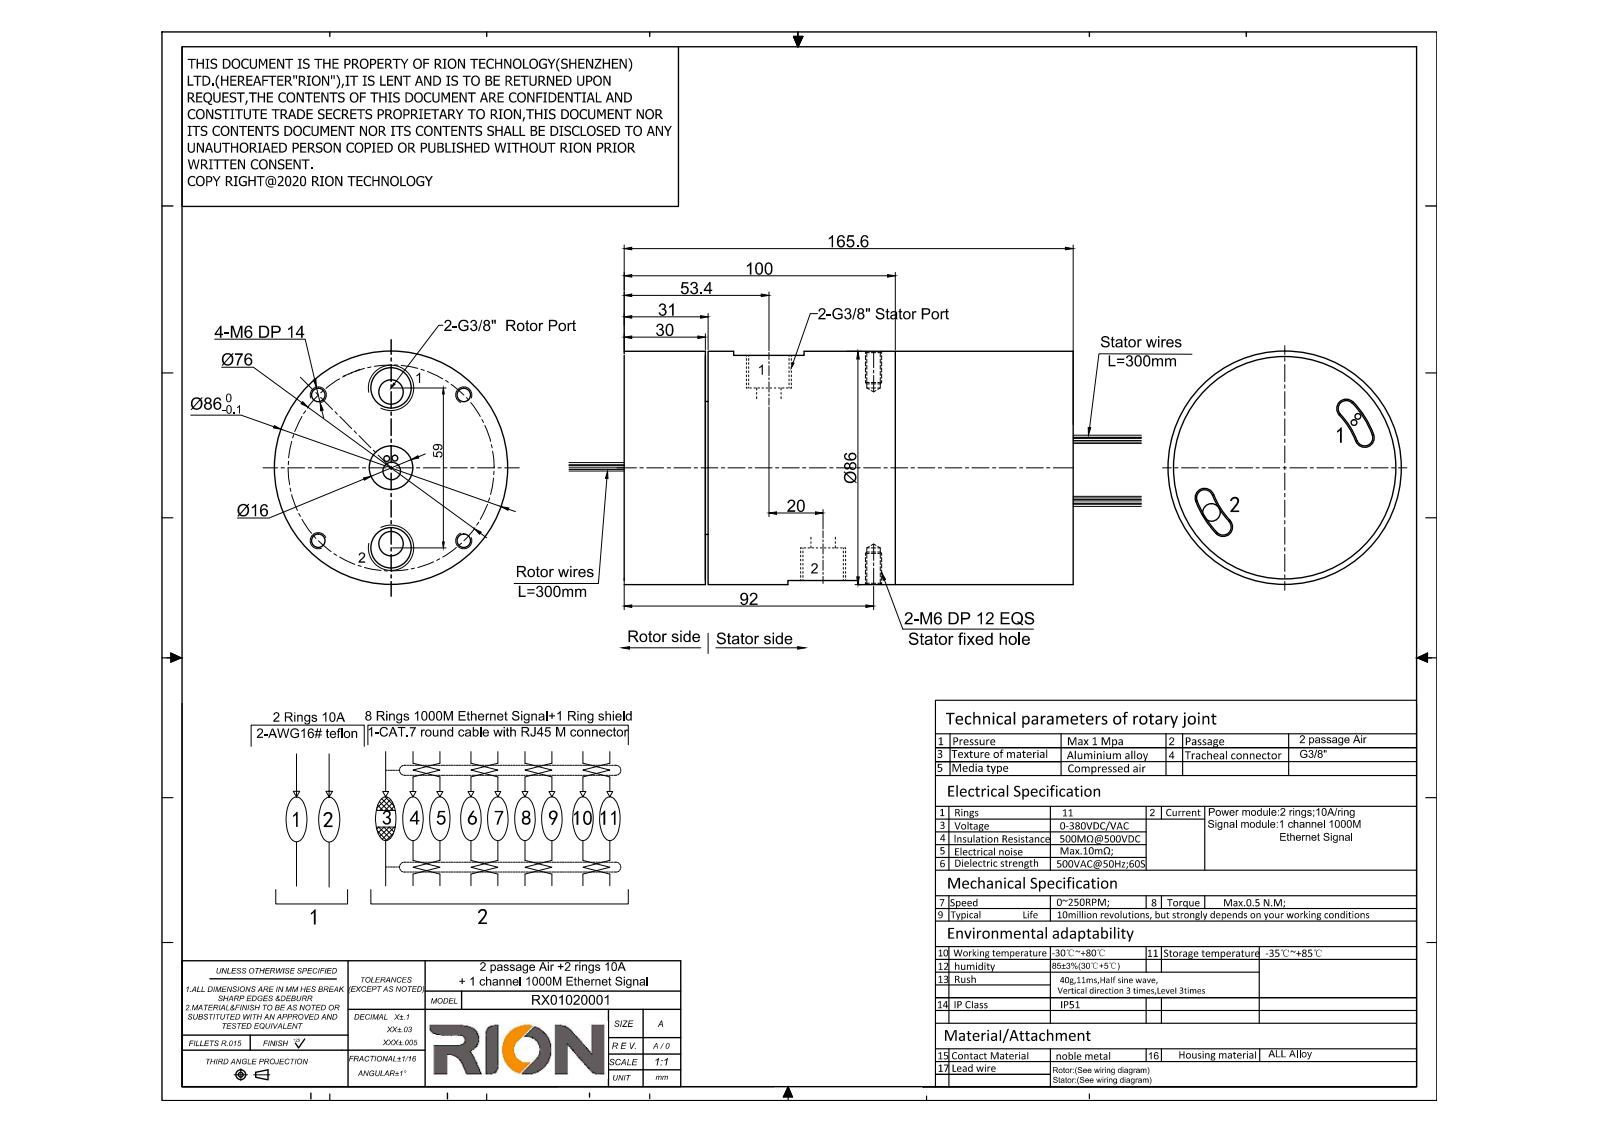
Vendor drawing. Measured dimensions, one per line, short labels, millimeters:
name: MKD23-P0210-S09
written by: SolidWorks 2014 (CONFIG_CONTROL_DESIGN)
unit: mm
bodies: 1 solid, 156 faces (34 planar, 84 cylindrical, 38 other)
size: 204.8 × 86 × 86
volume: 939 134 mm³; area: 80 147 mm²
holes: 9× ⌀5, 5× ⌀3.3, 4× ⌀9, 4× ⌀15.25, 1× ⌀16, 1× ⌀52, 1× ⌀82.1
bosses: 4× ⌀2.1, 1× ⌀86, 1× ⌀82, 1× ⌀49, 1× ⌀40, 1× ⌀6.5, 1× ⌀5.75
rounds: 4× R3, 1× R28.5, 1× R34.5
face distances: 1, 165.6, 134.6, 30, 31, 135.6, 69, 65.6, 100, 70
hole spacings: 38, 14.83, 15.58, 16.19, 26.89, 27, 27.36, 39.21
